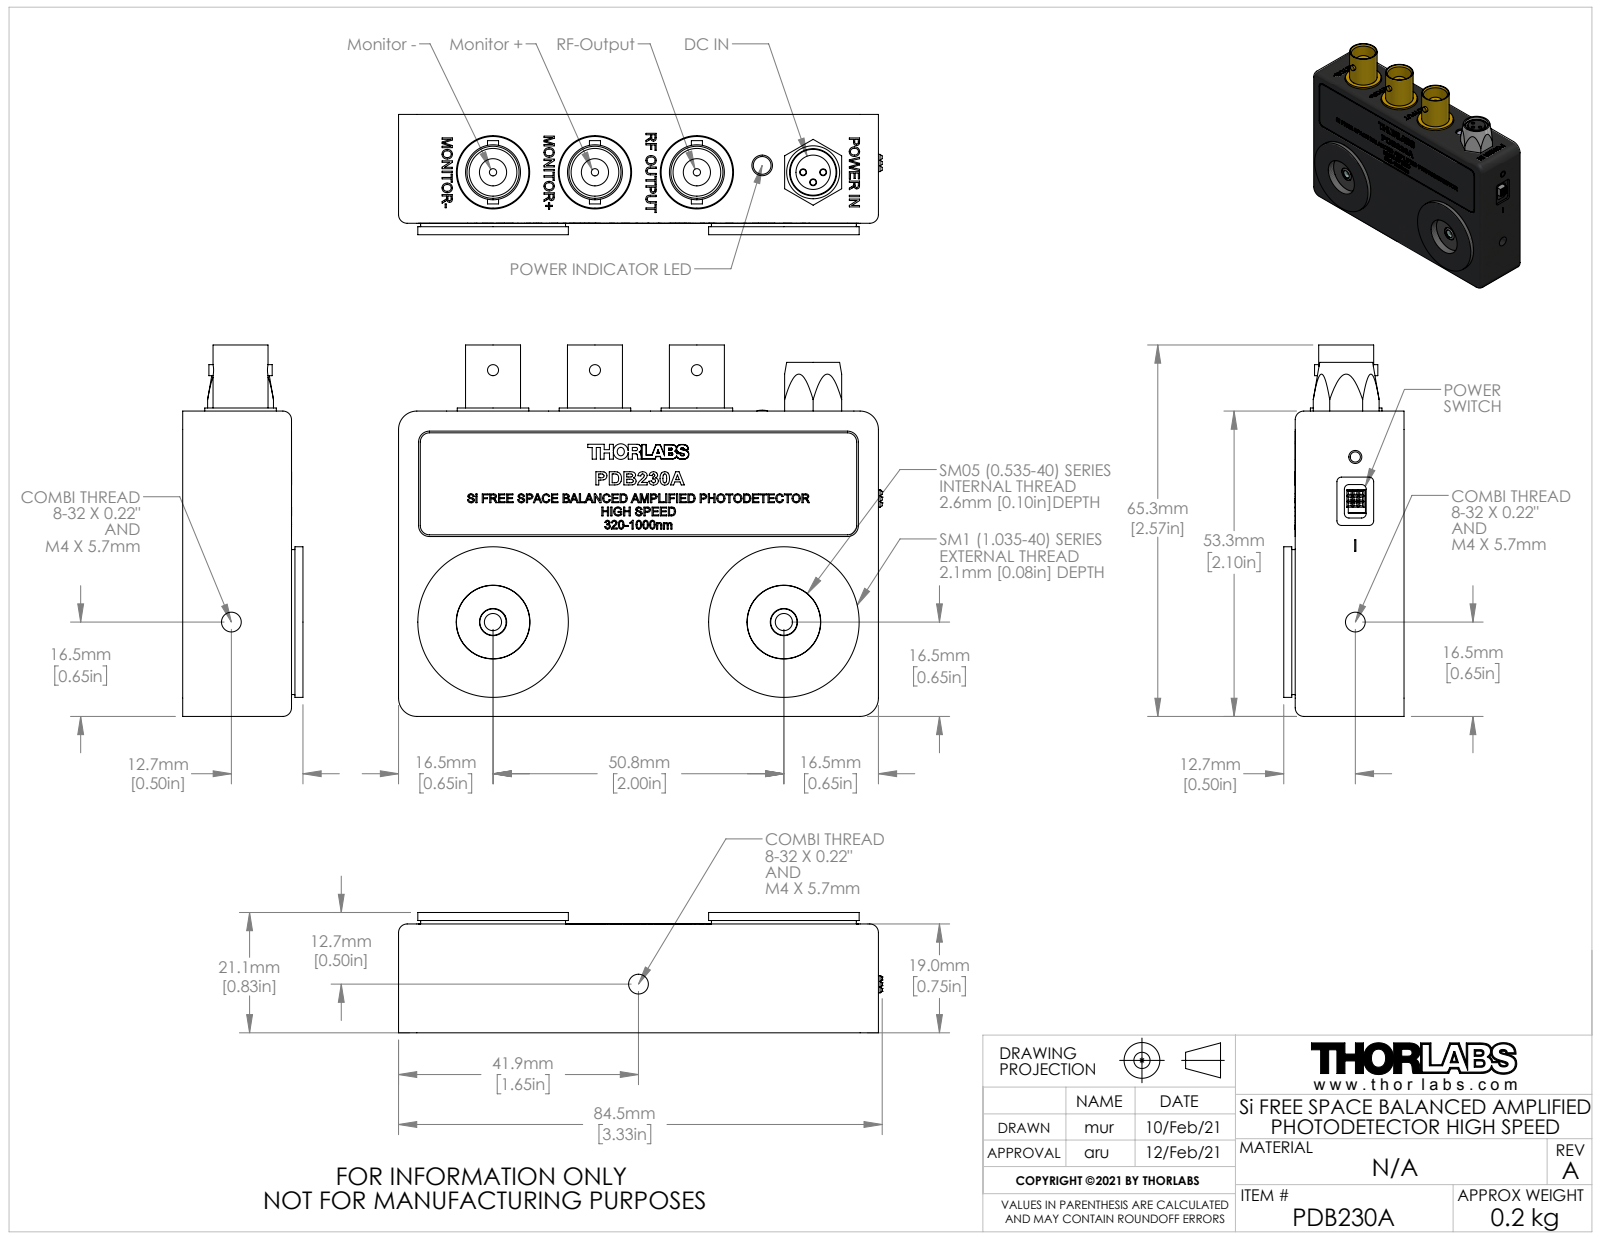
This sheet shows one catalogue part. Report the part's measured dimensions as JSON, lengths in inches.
{"part_name": "21.06.11_PDB230A_WEB", "step_written_by": "SolidWorks 2019 (AUTOMOTIVE_DESIGN)", "units": "inches", "bodies": {"solids": 17, "faces": 6029, "planar": 3592, "cylindrical": 332, "other": 2105}, "overall_size": [3.325, 2.552, 0.827], "volume_in3": 2.274, "surface_area_in2": 63.24, "round_holes": [[0.063, 9], [0.028, 8], [0.03, 6], [0.04, 6], [0.02, 5], [0.008, 4], [0.039, 4], [0.094, 4], [0.05, 3], [0.091, 3], [0.328, 3], [0.48, 3]], "round_bosses_or_shafts": [[0.017, 6], [0.079, 4], [0.492, 3], [0.378, 3], [0.37, 3], [0.187, 3], [0.157, 3], [0.091, 3]], "partial_cylinders_radius": [[0.126, 31], [0.006, 24], [0.016, 24], [0.13, 14], [0.031, 8], [0.02, 6], [0.075, 6], [0.098, 5]], "face_to_face_distances": [0.063, 0.45, 0.748, 0.685, 0.062, 0.235, 0.513, 0.071, 0.164, 0.677], "hole_center_spacings": [0.079, 0.044, 0.069, 0.071, 0.126, 0.656, 1.506, 0.098]}
